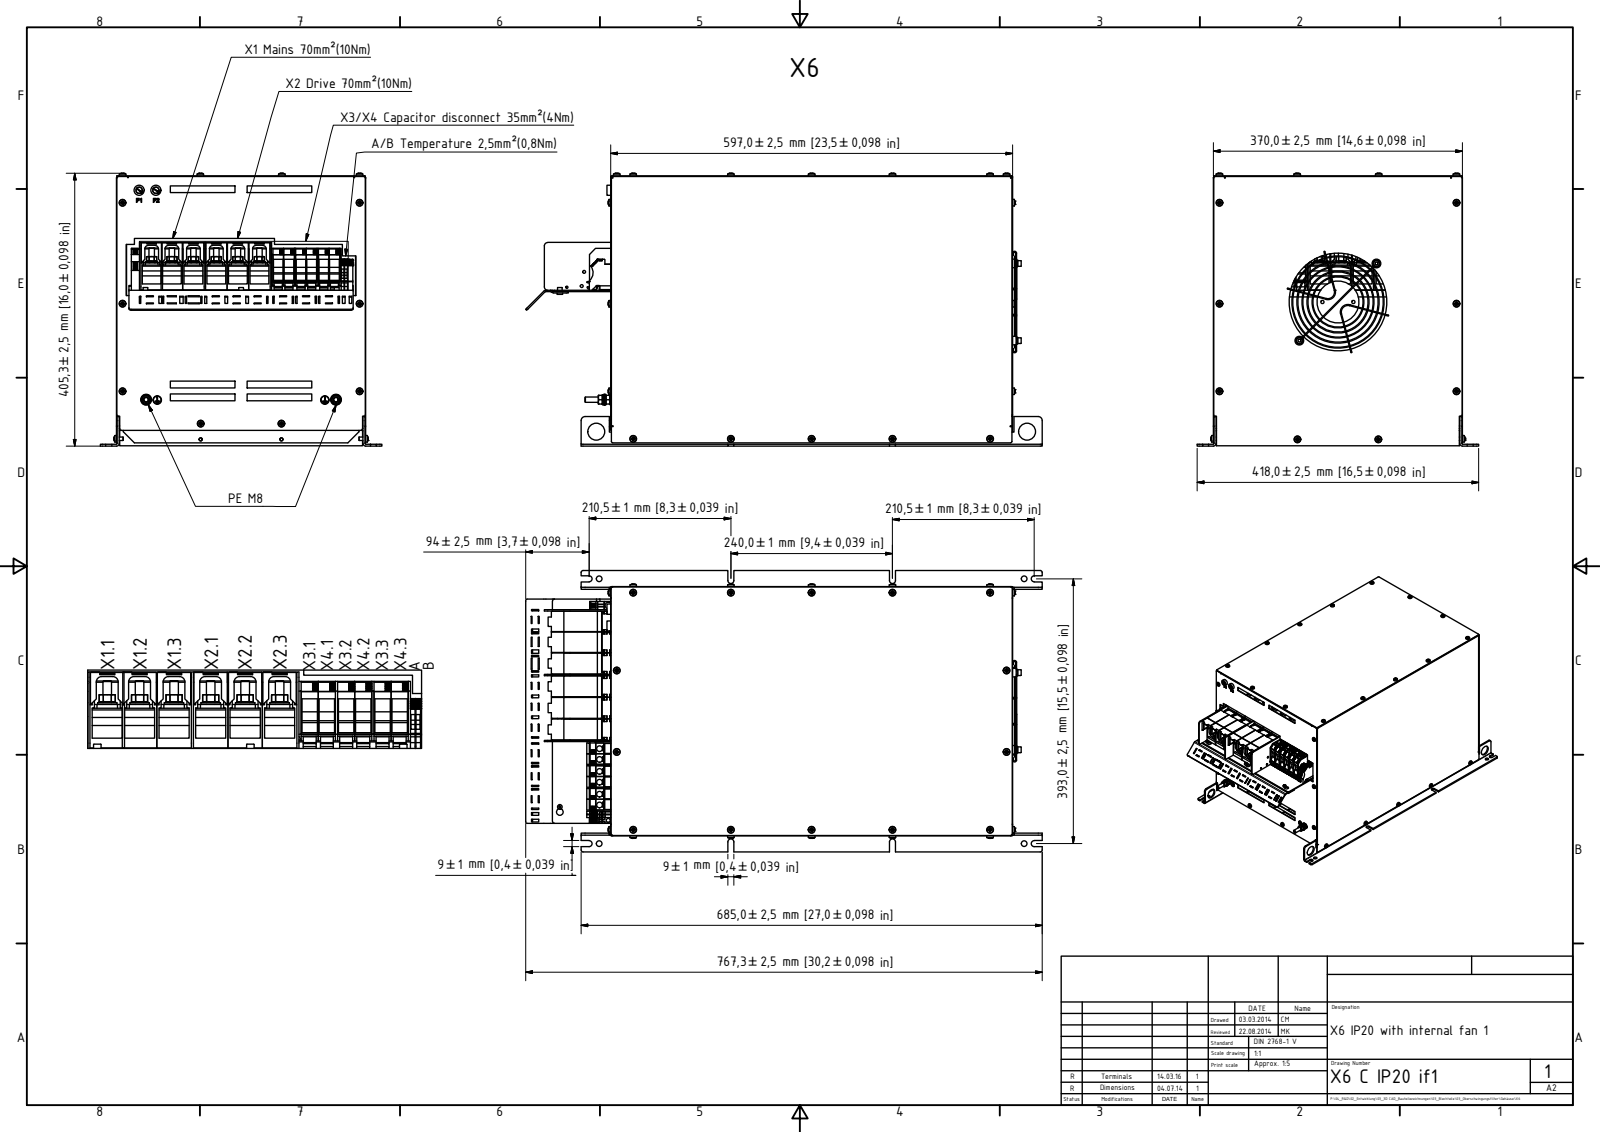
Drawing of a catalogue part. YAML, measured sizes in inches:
part_name: "10100398 Deckel X5_X6; 10100402 Seitenwand X6; 10100400 Anschlussblech X6; 10100401 Lüfterblech X6 (+8 more)"
step_written_by: "Autodesk Inventor 2015 (AUTOMOTIVE_DESIGN)"
units: inches
bodies: {solids: 123, faces: 9228, planar: 5509, cylindrical: 2224, other: 1495}
overall_size: [30.207, 16.457, 15.957]
volume: 194.4
surface_area: 5321
round_holes:
  - {diameter: 0.163, count: 27}
  - {diameter: 0.256, count: 27}
  - {diameter: 0.325, count: 12}
  - {diameter: 0.276, count: 9}
  - {diameter: 0.354, count: 8}
  - {diameter: 0.128, count: 7}
  - {diameter: 0.335, count: 6}
  - {diameter: 0.157, count: 5}
  - {diameter: 0.236, count: 5}
  - {diameter: 0.177, count: 4}
  - {diameter: 0.323, count: 4}
  - {diameter: 0.394, count: 3}
round_bosses_or_shafts:
  - {diameter: 0.197, count: 31}
  - {diameter: 0.181, count: 29}
  - {diameter: 0.315, count: 14}
  - {diameter: 0.709, count: 12}
  - {diameter: 0.055, count: 8}
  - {diameter: 0.335, count: 5}
  - {diameter: 0.362, count: 4}
  - {diameter: 0.276, count: 3}
partial_cylinders:
  - {radius: 0.009, count: 112}
  - {radius: 0.039, count: 68}
  - {radius: 0.02, count: 64}
  - {radius: 0.006, count: 54}
  - {radius: 0.079, count: 49}
  - {radius: 0.004, count: 37}
  - {radius: 0.004, count: 33}
  - {radius: 0.128, count: 28}
face_to_face_distances: [0.039, 14.528, 14.488, 14.567, 0.118, 23.465, 0.079, 14.882, 14.843, 14.764]
hole_center_spacings: [0.827, 4.724, 13.858, 1.432, 5.709, 10.433, 15.157, 1.063]
